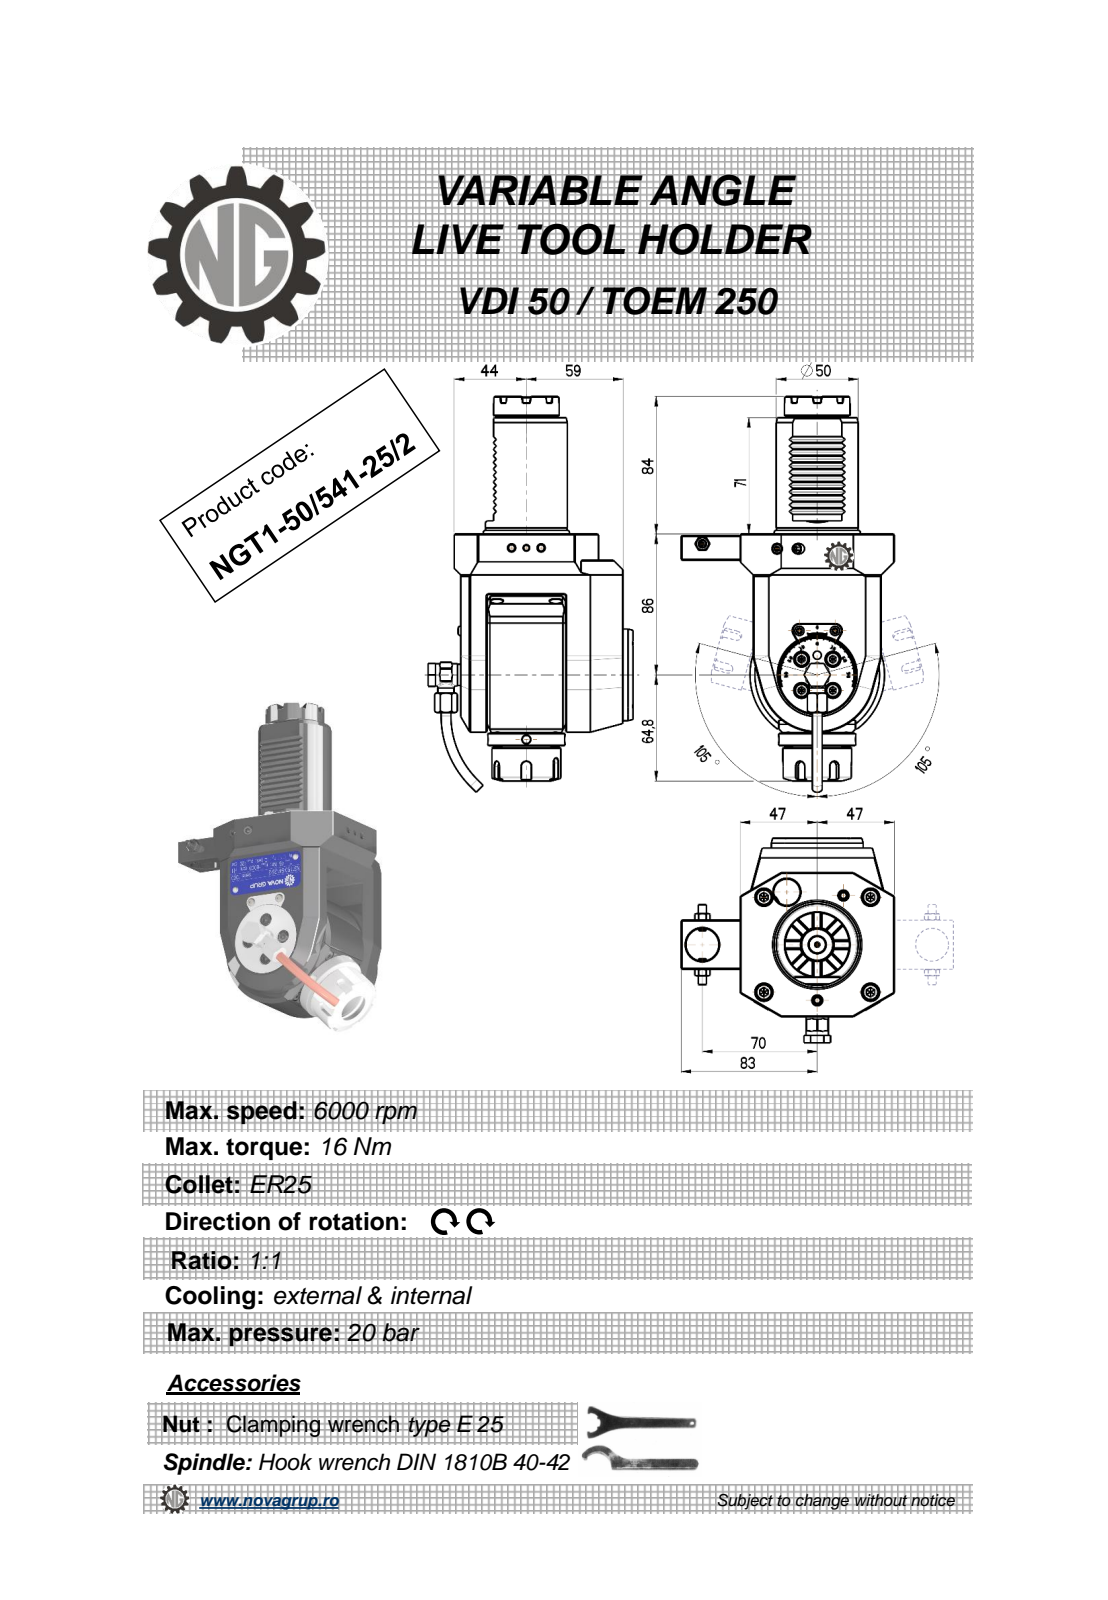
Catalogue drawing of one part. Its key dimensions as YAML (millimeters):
part_name: "NGT1_50_541_25_2"
step_written_by: "PRO/ENGINEER BY PARAMETRIC TECHNOLOGY CORPORATION, 2010280 (CONFIG_CONTROL_DESIGN)"
units: millimeters
bodies: {solids: 1, faces: 684, planar: 310, cylindrical: 140, other: 234}
overall_size: [241.67, 130, 124.9]
volume: 1039000
surface_area: 93179
round_holes:
  - {diameter: 4, count: 3}
  - {diameter: 5, count: 2}
  - {diameter: 3, count: 1}
  - {diameter: 6.2, count: 1}
  - {diameter: 9, count: 1}
  - {diameter: 9.5, count: 1}
  - {diameter: 10, count: 1}
  - {diameter: 11, count: 1}
  - {diameter: 20, count: 1}
  - {diameter: 20.3, count: 1}
round_bosses_or_shafts:
  - {diameter: 6, count: 2}
  - {diameter: 5.7, count: 2}
  - {diameter: 56, count: 1}
  - {diameter: 50, count: 1}
  - {diameter: 47, count: 1}
  - {diameter: 42, count: 1}
  - {diameter: 40, count: 1}
  - {diameter: 35, count: 1}
partial_cylinders:
  - {radius: 0.26, count: 12}
  - {radius: 0.3, count: 12}
  - {radius: 0.16, count: 6}
  - {radius: 3, count: 5}
  - {radius: 0.5, count: 4}
  - {radius: 1, count: 2}
  - {radius: 10, count: 2}
  - {radius: 7.7, count: 1}
face_to_face_distances: [37, 99, 16, 8, 6, 21, 64, 105, 20, 4]
hole_center_spacings: [0.4, 39.45, 49, 49.4, 70, 85.45, 85.68, 116.95]
